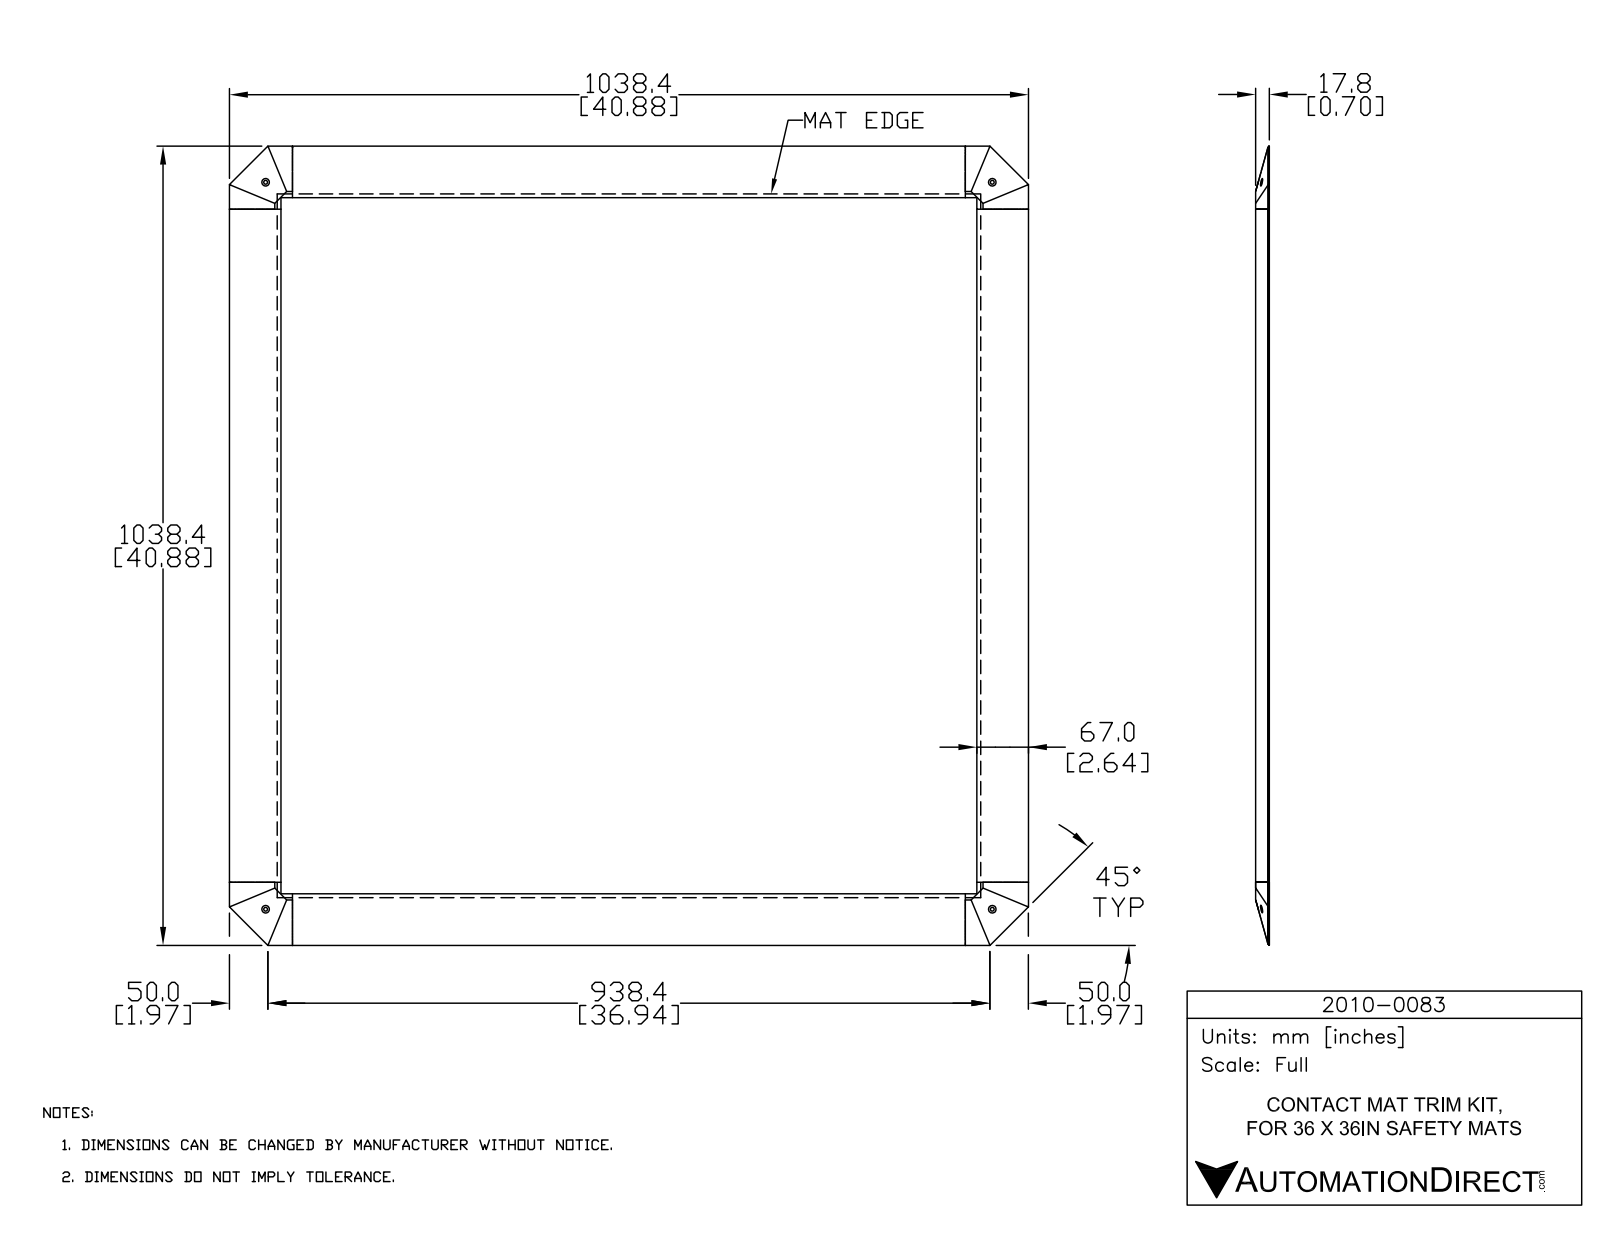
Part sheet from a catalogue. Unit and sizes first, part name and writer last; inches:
Units: inches
Overall size (bounding box): 40.882 × 40.882 × 0.701
Round holes (diameter × count): ⌀0.197 ×4, ⌀0.386 ×4
Round bosses / shafts (diameter × count): ⌀0.394 ×4
Partial cylindrical surfaces — rounded edges, fillets, slot ends (radius × count): R0.008 ×200, R0.039 ×108, R0.02 ×60, R0.017 ×8, R0.512 ×8, R0.291 ×4, R0.394 ×4
Main face-to-face distances: 0.114, 0.076, 0.038, 0.118, 0.19, 36.787, 0.63, 0.304, 0.079, 0.038
Hole centre spacings: 37.181, 52.582
Volume: 67.59 in³ · Surface area: 1 334 in²
Bodies: 1 solid, 2109 faces (1613 planar, 440 cylindrical, 56 other)
Part name (STEP PRODUCT): 2010-0083
STEP written by: SolidWorks 2018 (AUTOMOTIVE_DESIGN)
